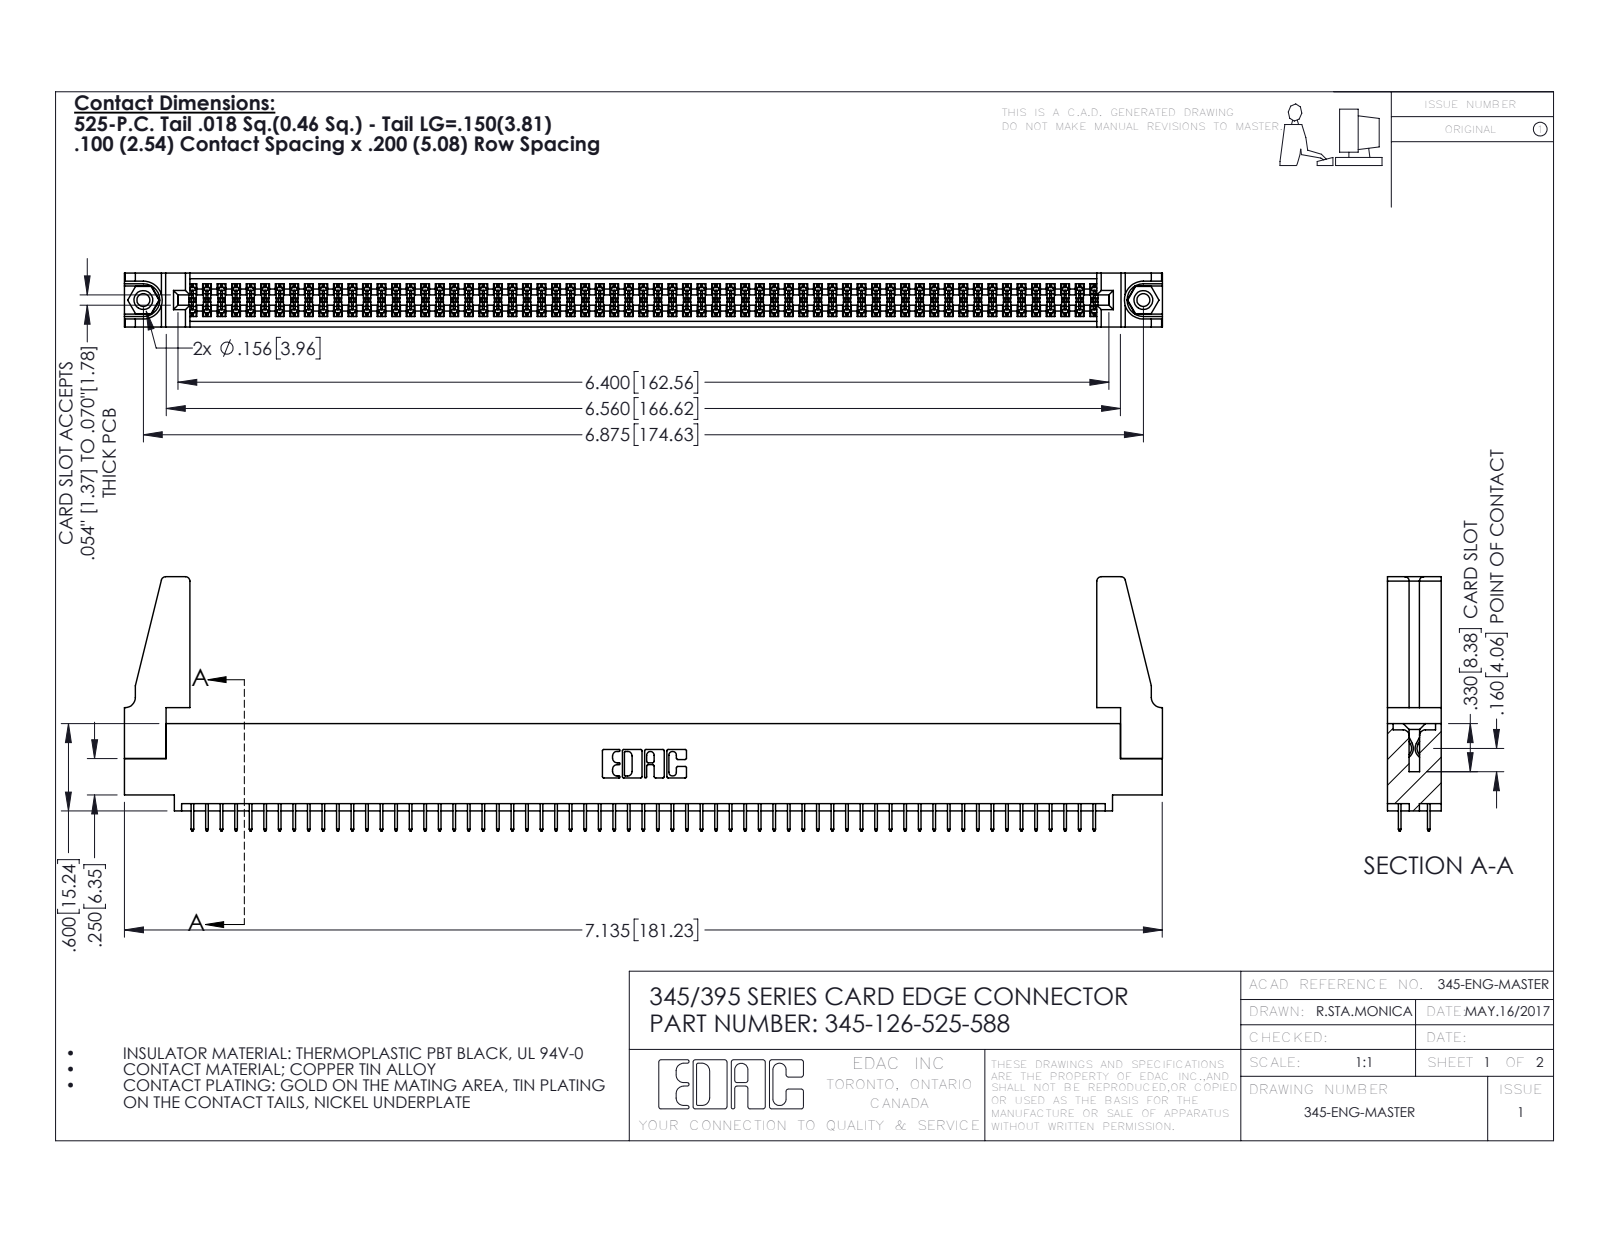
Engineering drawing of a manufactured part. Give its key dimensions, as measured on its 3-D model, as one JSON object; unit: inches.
{"part_name": "345-250-001_345-250-001-102; 345-292-001_345-293-125; 345-126-525-588; 345-220-078_345-220-088 (+1 more)", "step_written_by": "SolidWorks 2020 (CONFIG_CONTROL_DESIGN)", "units": "inches", "bodies": {"solids": 131, "faces": 7058, "planar": 5070, "cylindrical": 1972, "other": 16}, "overall_size": [7.136, 1.747, 0.37], "volume_in3": 1.268, "surface_area_in2": 44.79, "round_holes": [[0.089, 2], [0.125, 2], [0.156, 2], [0.064, 1]], "round_bosses_or_shafts": [[0.155, 2]], "partial_cylinders_radius": [[0.006, 189], [0.01, 22], [0.03, 8], [0.007, 6], [0.031, 6], [0.026, 3], [0.014, 2], [0.019, 2]], "face_to_face_distances": [0.072, 0.298, 0.37, 0.2, 0.098, 0.272, 0.025, 0.225, 0.072, 0.175], "hole_center_spacings": [0.27, 6.639, 6.875]}
